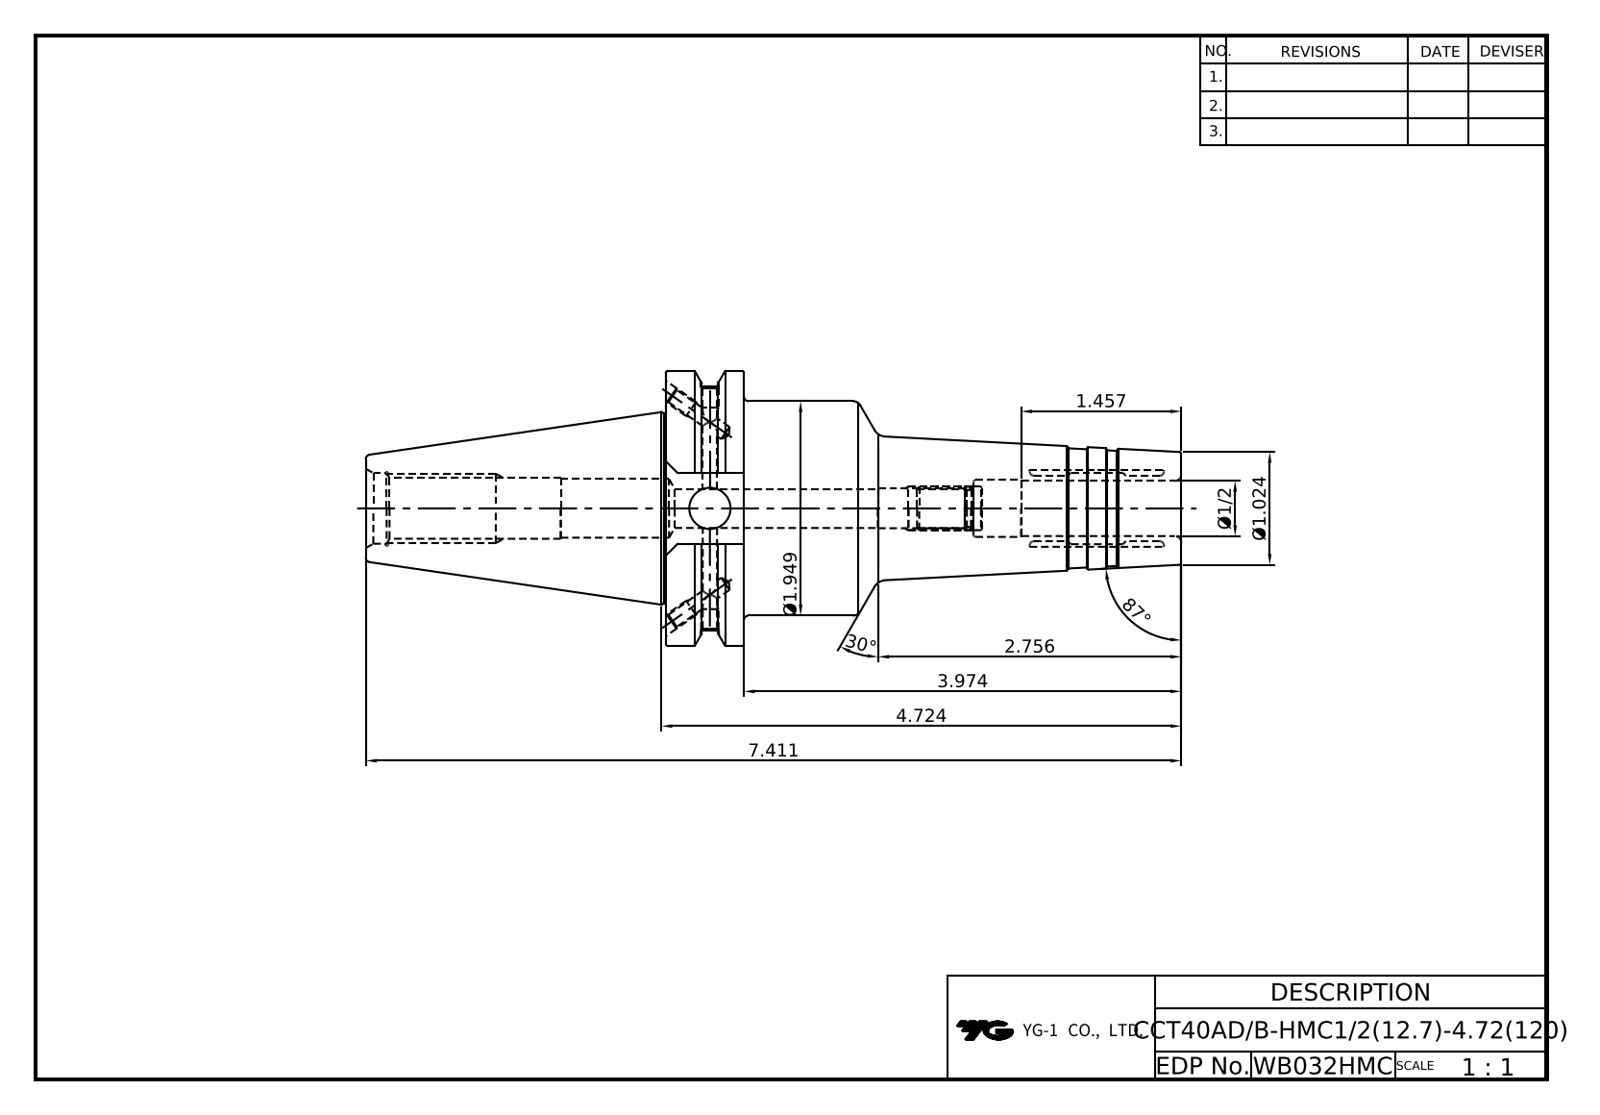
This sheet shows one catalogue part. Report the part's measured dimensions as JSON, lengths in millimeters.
{"part_name": "LO-CCT40ADB-HMC12.7-4.72", "step_written_by": "Autodesk Inventor 2024 (AUTOMOTIVE_DESIGN)", "units": "millimeters", "bodies": {"solids": 1, "faces": 106, "planar": 35, "cylindrical": 30, "other": 41}, "overall_size": [188.25, 63.5, 61.09], "volume_mm3": 200558, "surface_area_mm2": 34714, "round_holes": [[3.24, 4], [4, 2], [4.2, 2], [8.92, 1], [9.53, 1], [12.7, 1], [13, 1], [13.3, 1], [13.39, 1], [16.3, 1]], "round_bosses_or_shafts": [[63.5, 1], [49.5, 1], [43.8, 1]], "partial_cylinders_radius": [[8.19, 1], [28.15, 1]], "face_to_face_distances": [18.05, 119, 100.95, 47.6, 16.38, 69.25, 87.3, 188.25, 81.34, 12.09]}
